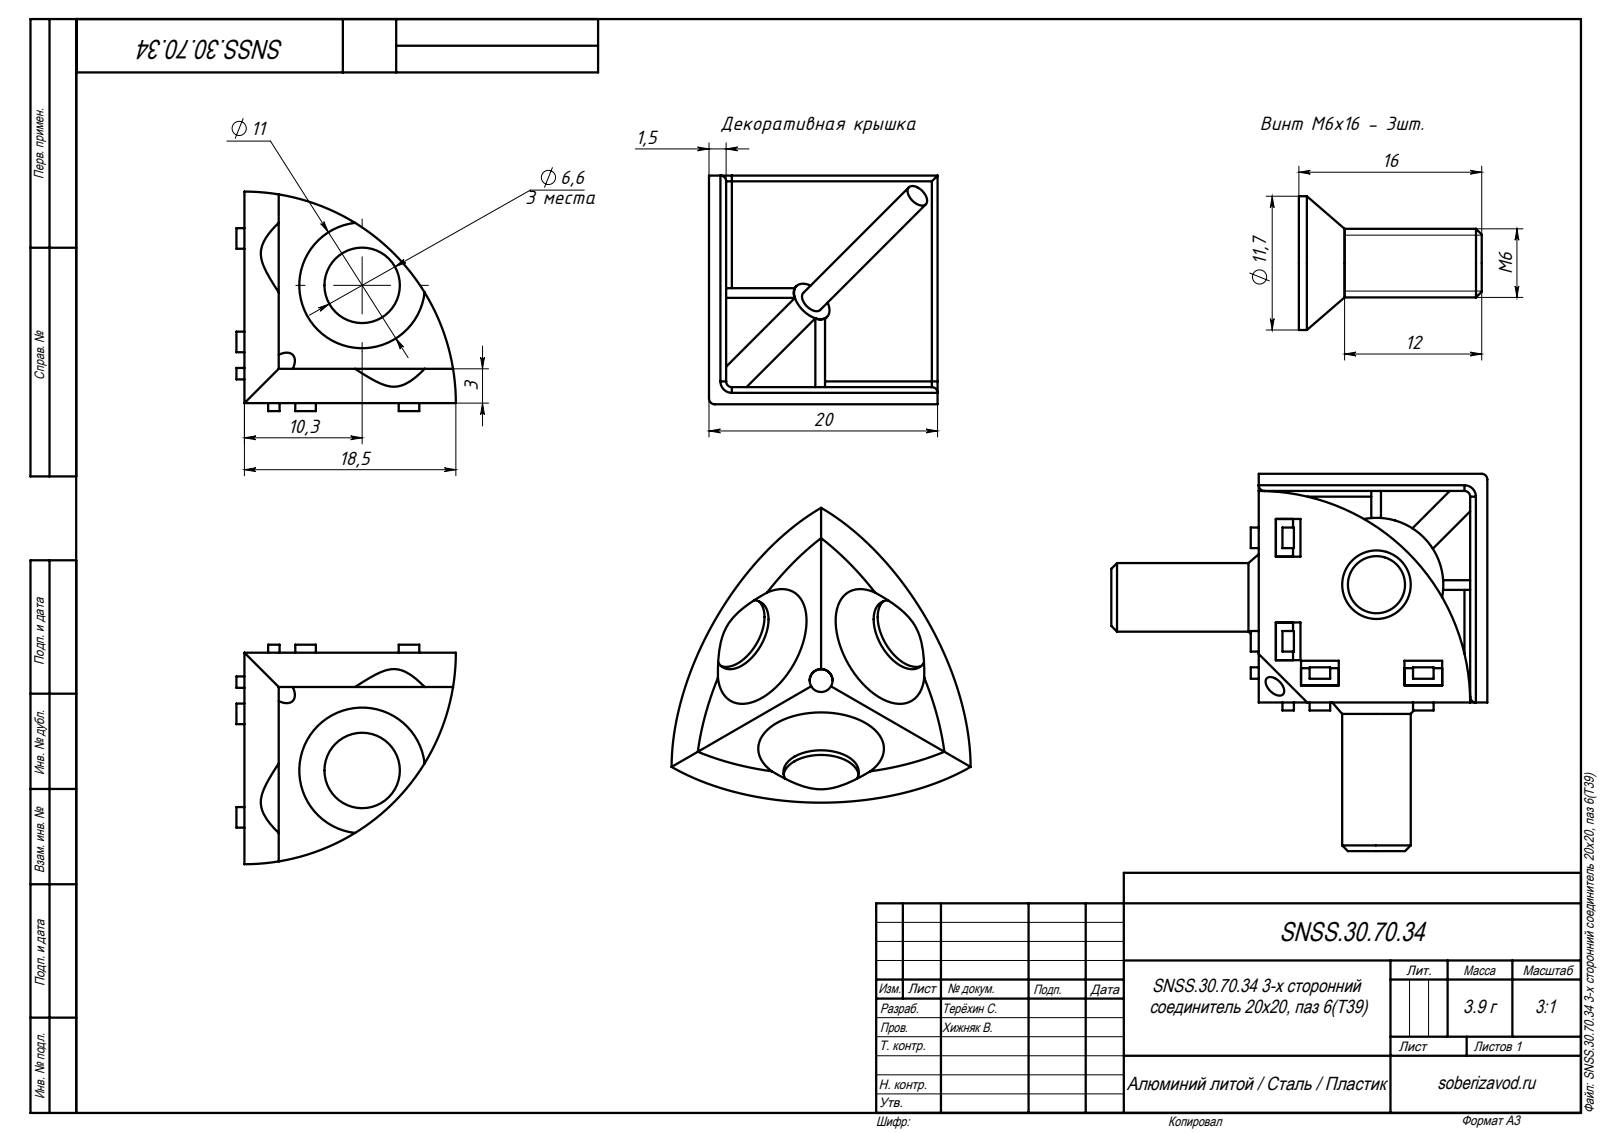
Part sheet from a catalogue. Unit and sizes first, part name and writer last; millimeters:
Units: millimetres
Overall size (bounding box): 32.3 × 32.3 × 32.3
Round holes (diameter × count): ⌀6.6 ×3, ⌀2 ×1, ⌀3.8 ×1
Round bosses / shafts (diameter × count): ⌀11.7 ×3, ⌀6 ×3, ⌀2.1 ×1
Partial cylindrical surfaces — rounded edges, fillets, slot ends (radius × count): R0.5 ×12, R18.5 ×3
Main face-to-face distances: 1.5, 18.5, 20, 0.7, 3.7, 14.8, 3, 16.3, 17, 15.5
Volume: 5 125 mm³ · Surface area: 6 179 mm²
Bodies: 20 solids, 361 faces (298 planar, 42 cylindrical, 21 other)
Part name (STEP PRODUCT): SNSS.30.70.34 3-х сторонний соединитель 20х20, паз 6(T39)
STEP written by: SolidWorks 2020 (AUTOMOTIVE_DESIGN)
